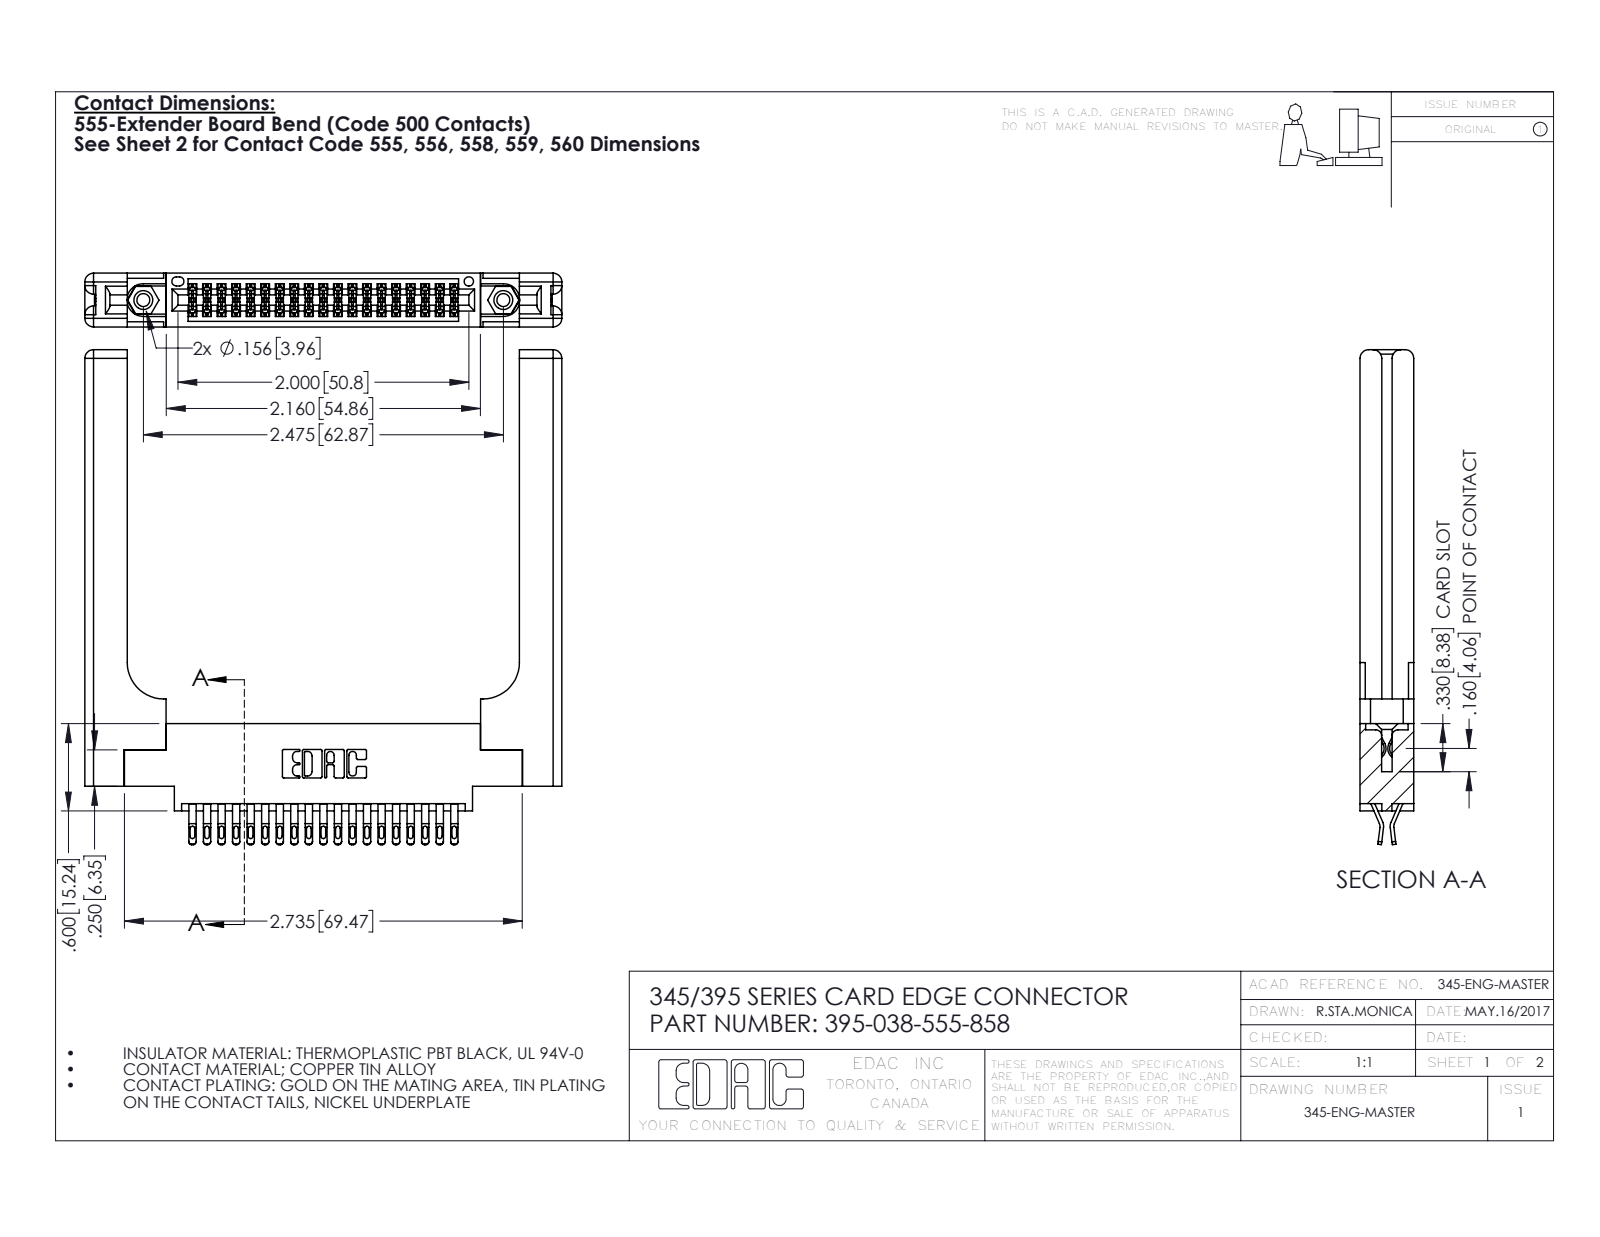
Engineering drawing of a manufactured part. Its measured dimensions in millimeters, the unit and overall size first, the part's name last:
Units: millimetres
Overall size (bounding box): 86.4 × 83.3 × 9.4
Round holes (diameter × count): ⌀2.3 ×2, ⌀3.2 ×2, ⌀4 ×2, ⌀1.6 ×1
Round bosses / shafts (diameter × count): ⌀3.9 ×2
Partial cylindrical surfaces — rounded edges, fillets, slot ends (radius × count): R0.4 ×95, R0.5 ×76, R0.2 ×57, R0.3 ×22, R1.5 ×16, R0.2 ×6, R0.8 ×6, R0.7 ×3
Main face-to-face distances: 9.4, 1.8, 7.6, 3.8, 3.8, 2, 0.6, 5.6, 5.7, 3.1
Hole centre spacings: 6.9, 56.9, 62.9
Volume: 16 400 mm³ · Surface area: 16 780 mm²
Bodies: 43 solids, 2514 faces (1410 planar, 1044 cylindrical, 60 other)
Part name (STEP PRODUCT): 345 Part_0.170 Offset - 0.156 Dia-TH; 345-250-001_345-250-001-102; 345-292-001_555 Tail; 395-038-555-858 (+1 more)
STEP written by: SolidWorks 2016 (CONFIG_CONTROL_DESIGN)
